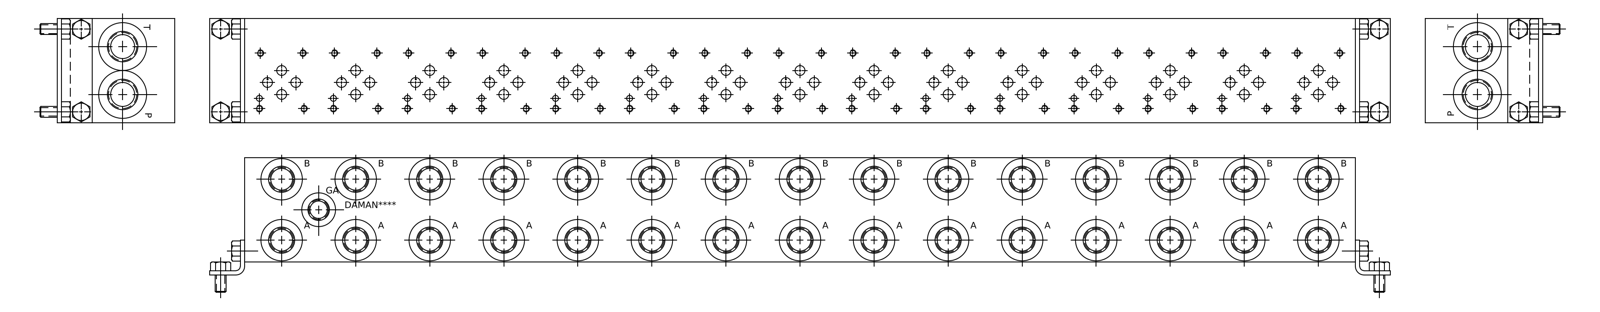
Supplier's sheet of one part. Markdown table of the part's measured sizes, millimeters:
| quantity | value |
| --- | --- |
| part name | Part_AD03P152S_3D |
| STEP written by | Autodesk Inventor 2020 (AUTOMOTIVE_DESIGN) |
| units | millimeters |
| bodies | 1 solid, 1802 faces (803 planar, 381 cylindrical, 618 other) |
| overall size | 809.62 × 76.2 × 76.2 |
| volume | 4 430 000 mm³ |
| surface area | 329 311 mm² |
| round holes (diameter × count) | 3.78 × 60, 4.83 × 60, 7.14 × 45, 14.3 × 30, 17.5 × 30, 19.05 × 30, 19.25 × 30, 30.63 × 30, 3.96 × 15, 6.35 × 15, 6.53 × 2, 7.92 × 2 |
| main face-to-face distances | 76.2, 0.79, 75.41, 809.62, 15.06, 14.27, 61.14, 808.83, 808.84, 808.05 |
| hole center spacings | 107.95, 215.9, 323.85, 116.74, 431.8, 220.43, 53.97, 53.98 |
